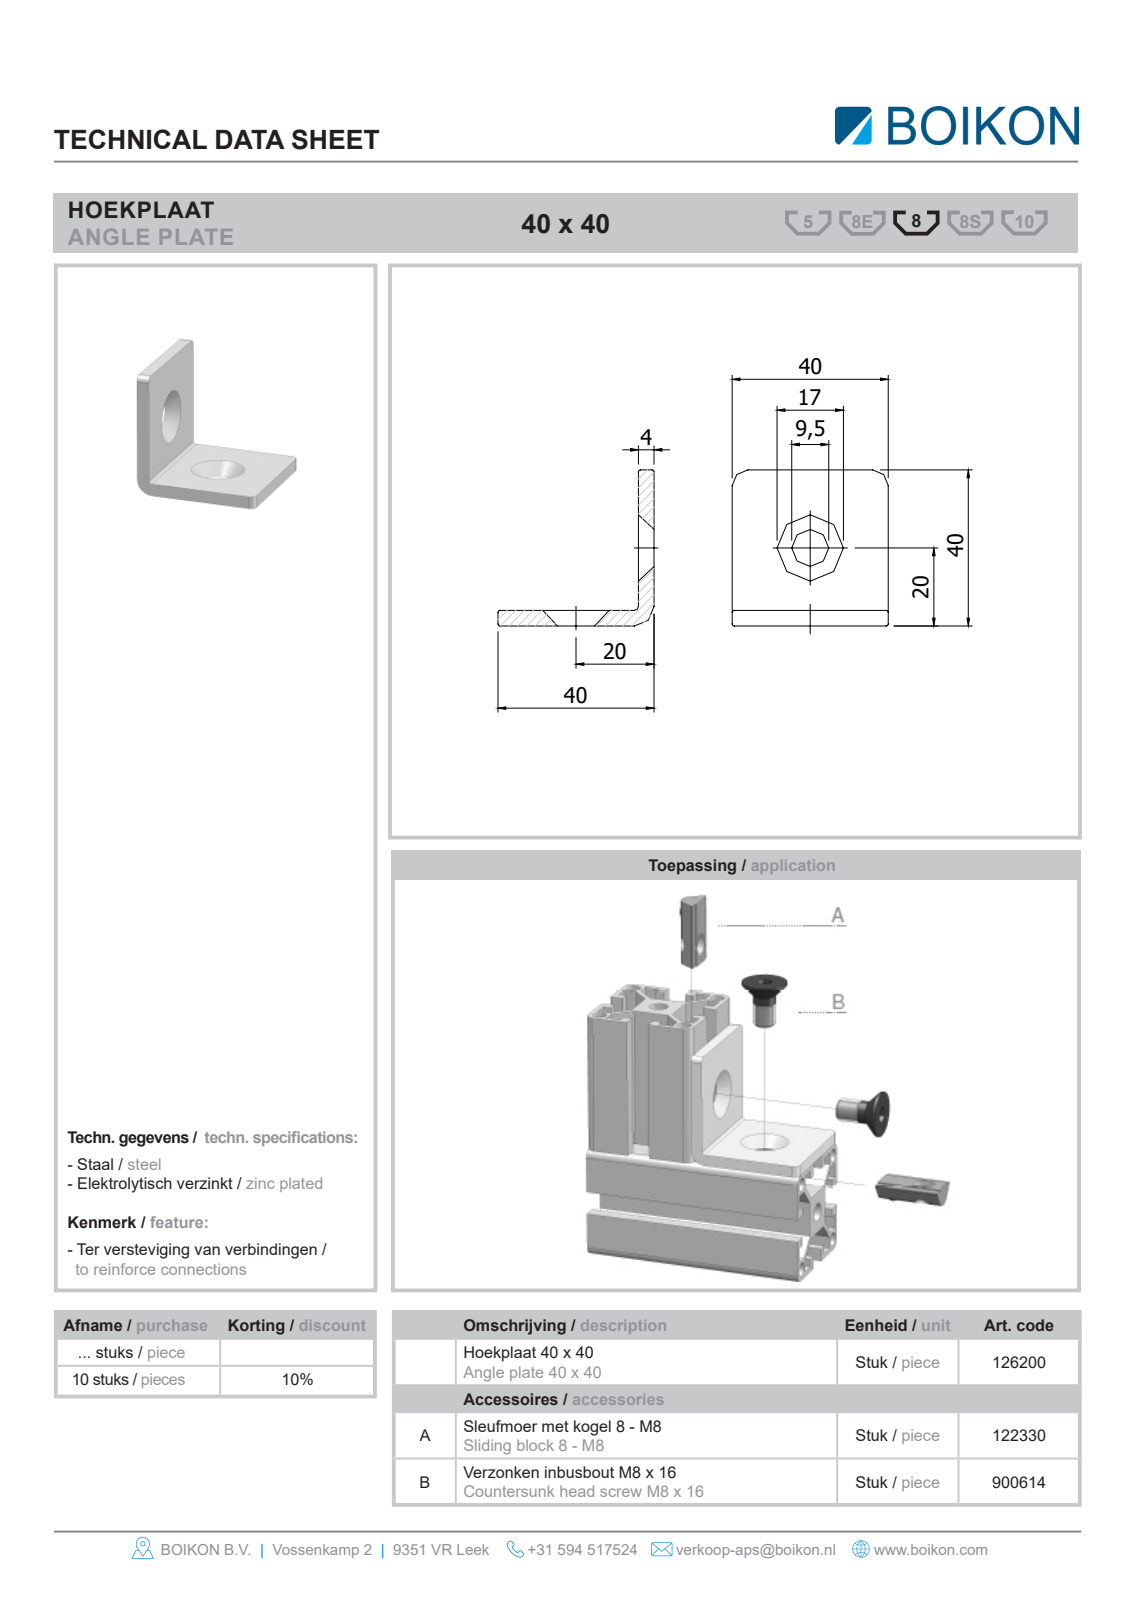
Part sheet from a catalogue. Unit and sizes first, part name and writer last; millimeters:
Units: millimetres
Overall size (bounding box): 52 × 52 × 40
Round holes (diameter × count): ⌀8 ×2
Round bosses / shafts (diameter × count): ⌀16 ×2, ⌀6.47 ×2
Partial cylindrical surfaces — rounded edges, fillets, slot ends (radius × count): R2 ×8, R0.5 ×4, R5 ×3, R1 ×1
Main face-to-face distances: 4, 40, 36, 3.97, 7.97, 43.97, 0.5, 4.47, 8.47, 44.47
Volume: 15 034 mm³ · Surface area: 10 202 mm²
Bodies: 5 solids, 92 faces (54 planar, 30 cylindrical, 8 other)
Part name (STEP PRODUCT): Root; 126200Plaat 40 x 40BOIKON; 900614Verz. inbusbout DIN 7991 EV M8 x 16BOIKON0; 122330Sleufmoer 8 - M8 met kogelBOIKON
STEP written by: HiCAD 2013 1802.4 Build 509 (AUTOMOTIVE_DESIGN)
